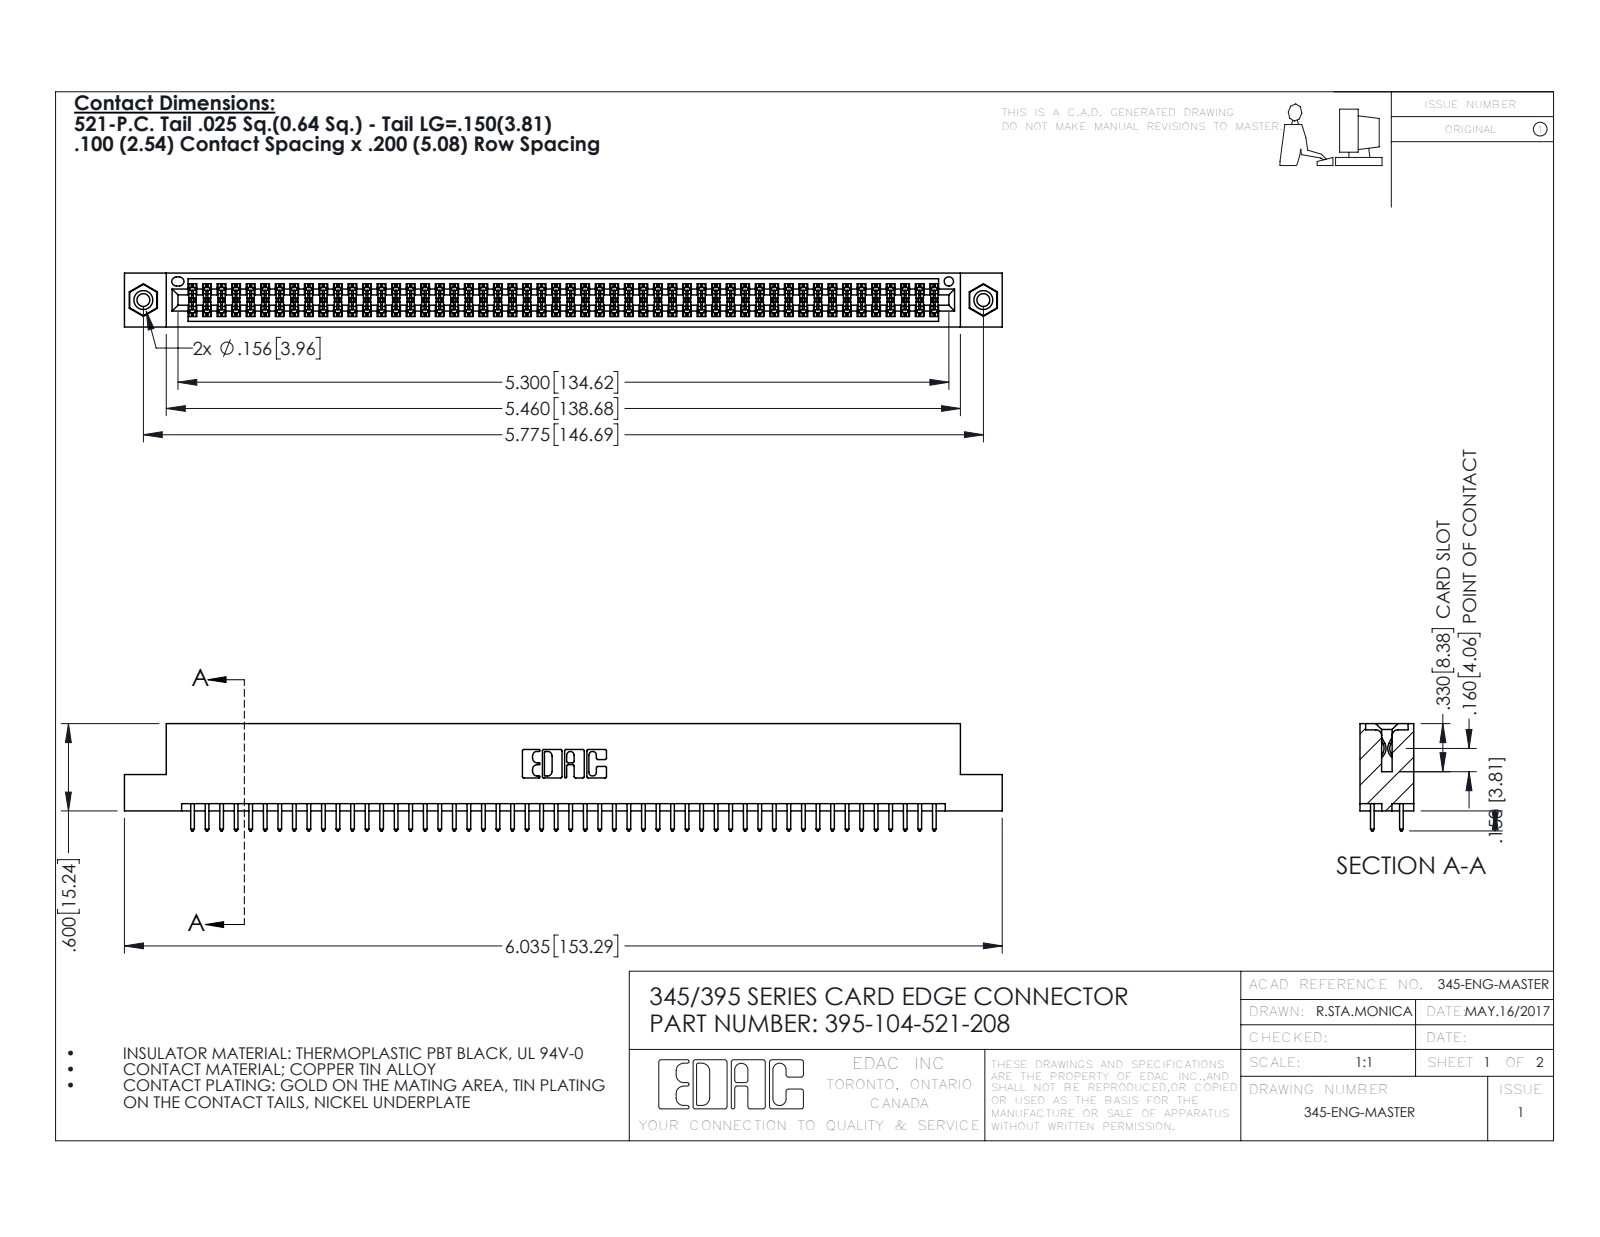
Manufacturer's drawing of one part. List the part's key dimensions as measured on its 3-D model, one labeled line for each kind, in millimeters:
Part name (STEP PRODUCT): 395-104-521-208; 345-292-001_345-293-121; 345-250-001_345-250-003-102; 345 Part_Flush Mounting Lugs - 0.156 Dia-TI
STEP written by: SolidWorks 2016 (CONFIG_CONTROL_DESIGN)
Units: millimetres
Bodies: 107 solids, 5386 faces (3544 planar, 1826 cylindrical, 16 other)
Overall size (bounding box): 153.3 × 18.7 × 9.4
Volume: 14 900 mm³ · Surface area: 22 010 mm²
Round holes (diameter × count): ⌀2.3 ×2, ⌀3.2 ×2, ⌀4 ×2, ⌀1.6 ×1
Round bosses / shafts (diameter × count): ⌀3.9 ×2
Partial cylindrical surfaces — rounded edges, fillets, slot ends (radius × count): R0.2 ×156, R0.3 ×104, R0.3 ×22, R0.2 ×6, R0.8 ×6, R0.7 ×3, R0.4 ×2, R0.5 ×2
Main face-to-face distances: 1.8, 7.6, 5.1, 9.4, 2.5, 6.9, 0.6, 5.7, 4.4, 3.8
Hole centre spacings: 6.9, 140.7, 146.7
